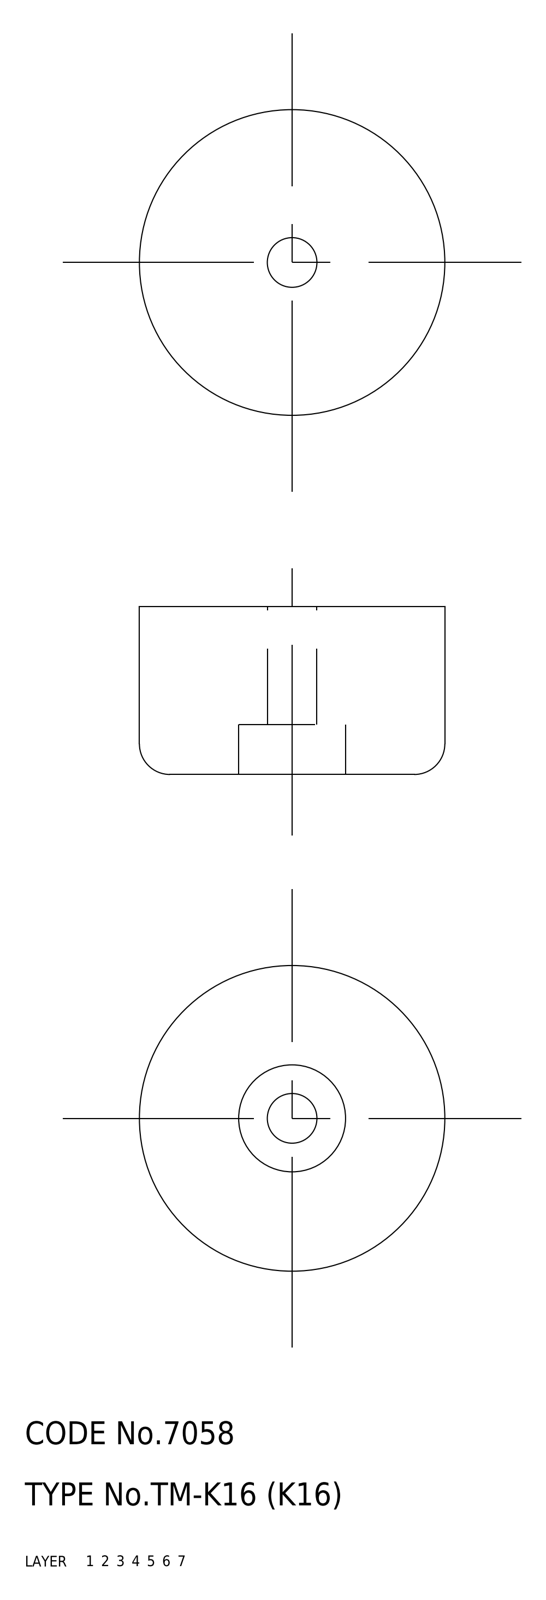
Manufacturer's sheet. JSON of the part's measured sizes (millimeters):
{"part_name": "rubber foot", "step_written_by": "CADfix (AUTOMOTIVE_DESIGN)", "units": "millimeters", "bodies": {"solids": 1, "faces": 11, "planar": 0, "cylindrical": 0, "other": 11}, "overall_size": [40, 40, 22], "volume_mm3": 25785, "surface_area_mm2": 5594}
